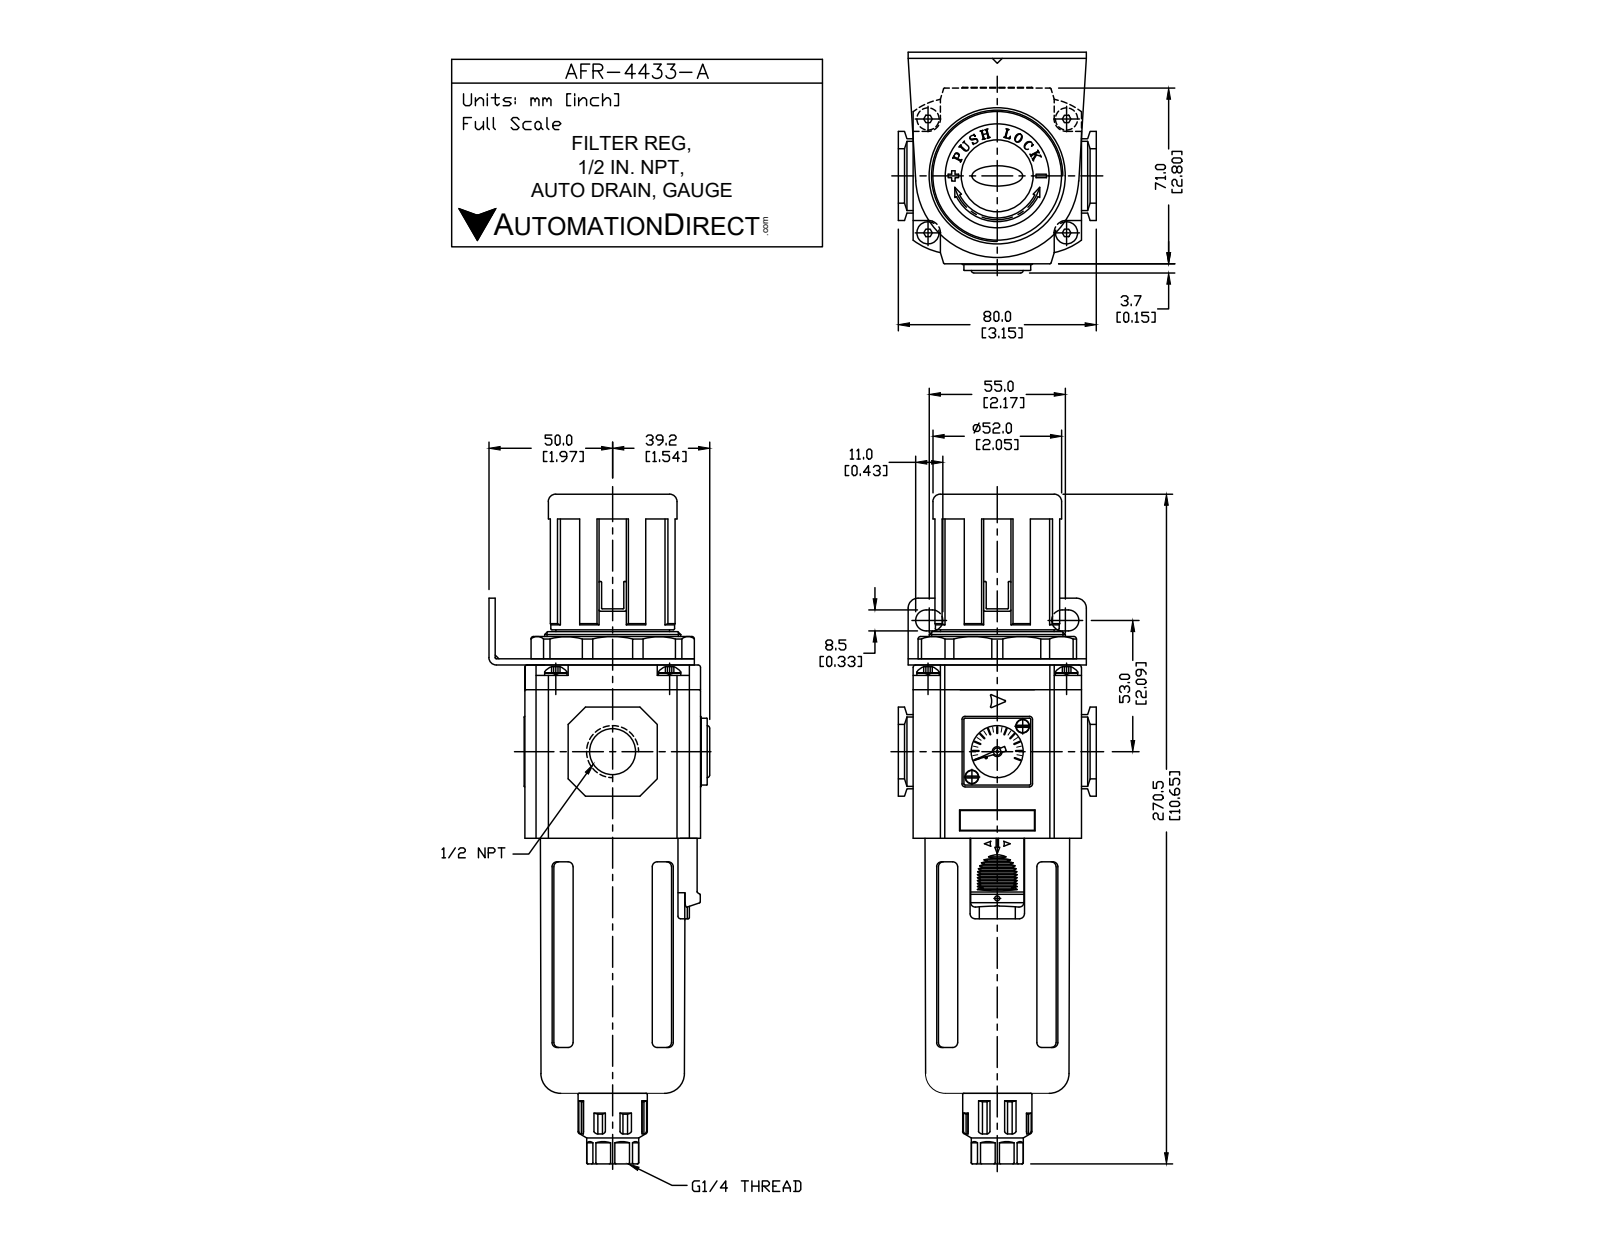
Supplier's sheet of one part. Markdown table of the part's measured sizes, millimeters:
| quantity | value |
| --- | --- |
| part name | AFR-4433-A |
| STEP written by | SolidWorks 2015 (CONFIG_CONTROL_DESIGN) |
| units | millimeters |
| bodies | 16 solids, 606 faces (371 planar, 169 cylindrical, 66 other) |
| overall size | 270.5 × 88.2 × 80 |
| volume | 561 874 mm³ |
| surface area | 115 559 mm² |
| round holes (diameter × count) | 3 × 6, 2 × 1, 12 × 1, 17.86 × 1, 21 × 1, 30 × 1, 50 × 1 |
| round bosses / shafts (diameter × count) | 9 × 4, 2.7 × 2, 58 × 1, 55 × 1, 52 × 1, 43.68 × 1, 28 × 1, 21 × 1 |
| partial cylindrical surfaces (radius × count) | 2.9 × 18, 1 × 12, 1.2 × 10, 0.5 × 9, 9.5 × 8, 0.3 × 4, 4.25 × 4, 6.3 × 4 |
| main face-to-face distances | 2.5, 70, 72.5, 71, 68, 74, 52.2, 4, 85.5, 15.5 |
| hole center spacings | 33.3, 14.5, 42.6, 51.2, 66.6, 28.99 |
